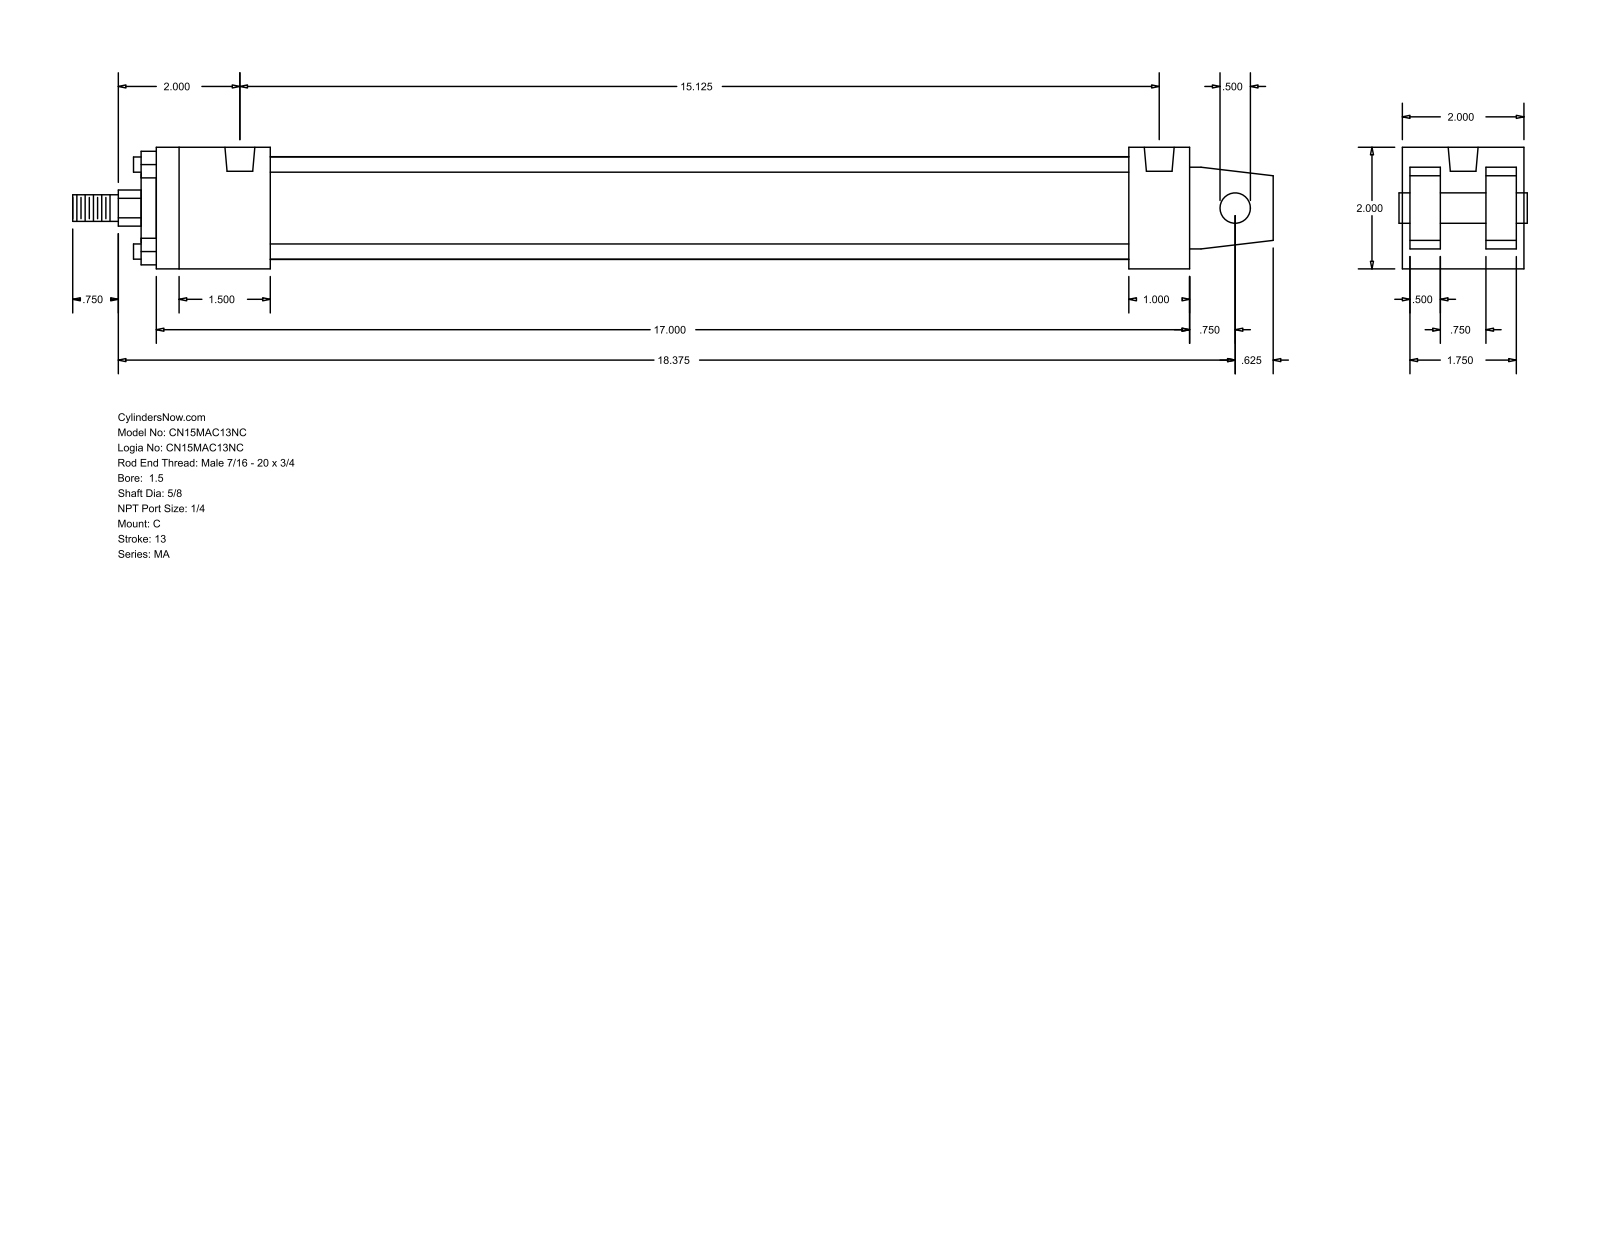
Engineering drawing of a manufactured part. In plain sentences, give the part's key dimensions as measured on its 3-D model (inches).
The part is named "MA_C__0150_0.625". Its 3-D file was written by "GSSL Pune (CONFIG_CONTROL_DESIGN)". It is 0 solids with 103 faces: 76 planar, 27 cylindrical and 0 other. Overall it measures 19.75 by 2 by 2 inches. Round holes: 4 of diameter 0.313, 2 of diameter 0.492. Round bosses or shafts: 4 of diameter 0.25, 1 of diameter 1.69, 1 of diameter 1.125, 1 of diameter 0.625, 1 of diameter 0.5, 1 of diameter 0.437. Partial cylindrical surfaces (rounded edges, fillets, slot ends): 1 of radius 0.297. The main face-to-face distances are 2, 0.5, 1.375, 0.625, 0.125, 1.875, 1.25, 17, 16, 1. The hole center spacings are 15.125.
